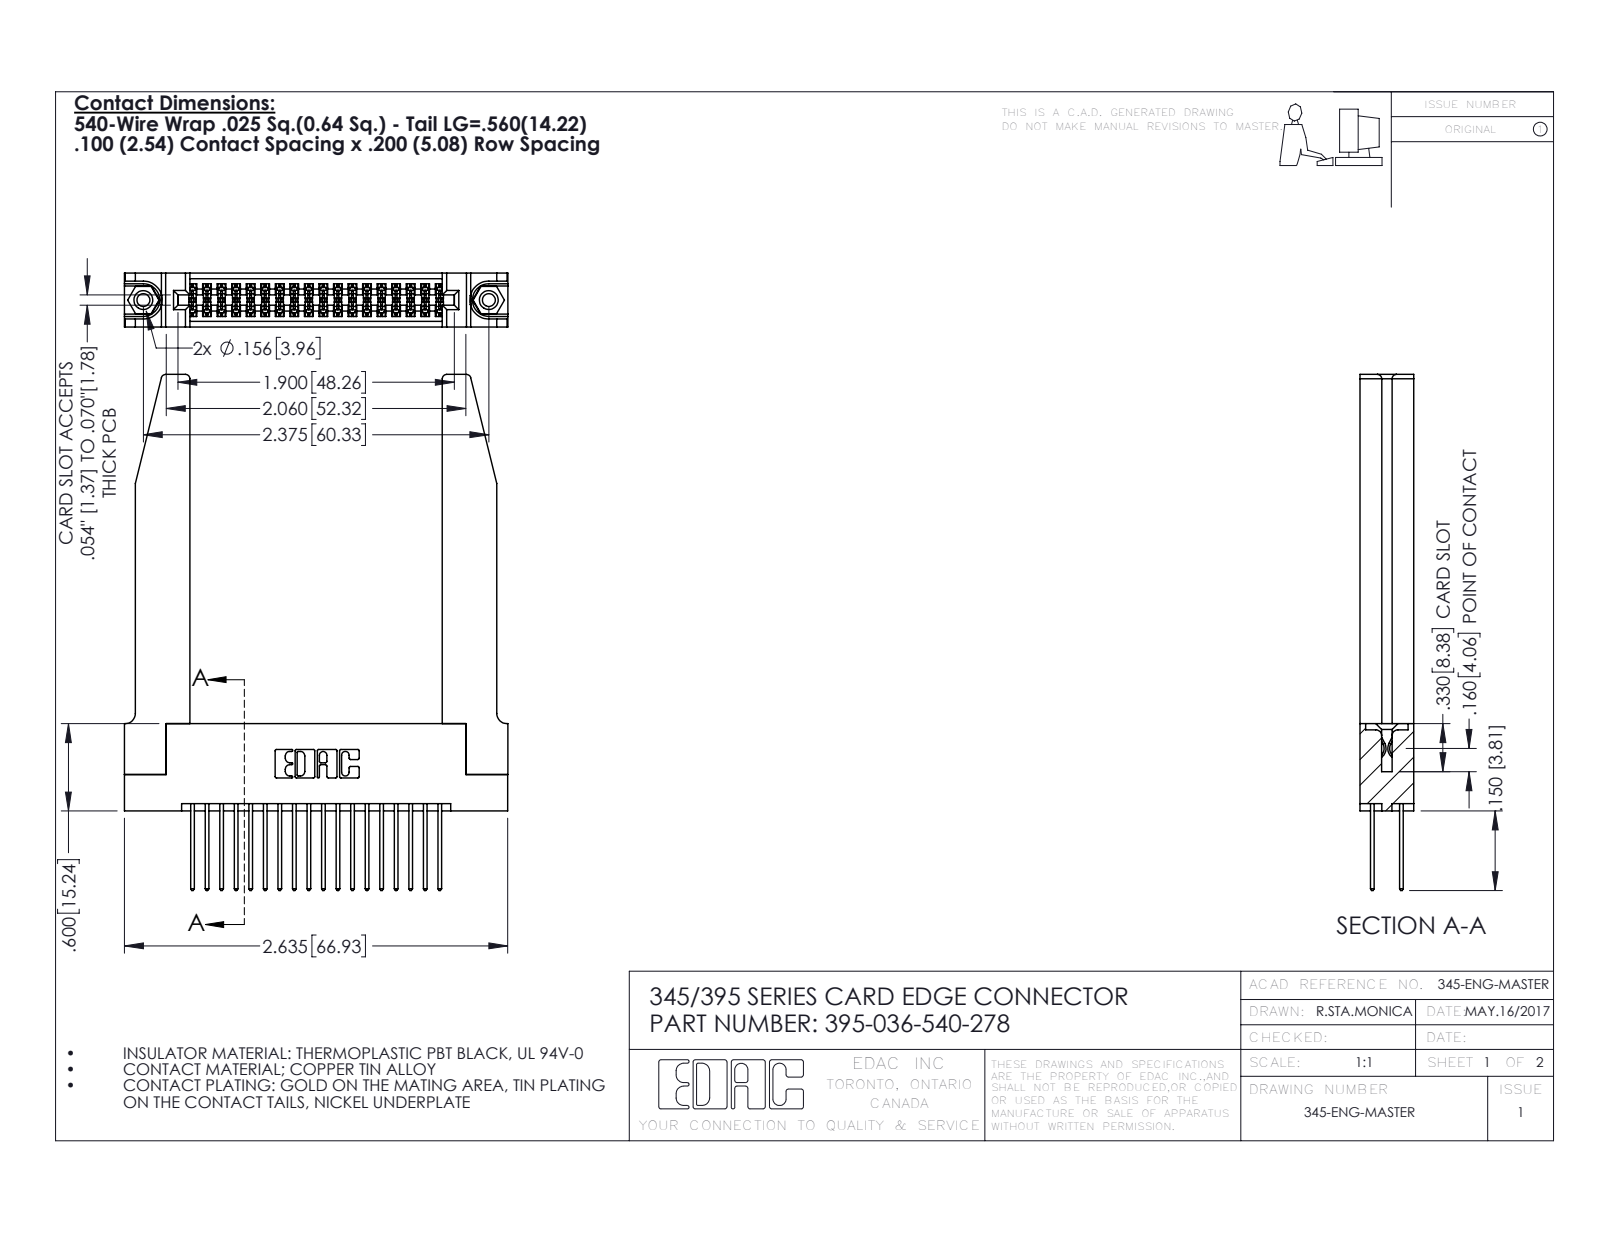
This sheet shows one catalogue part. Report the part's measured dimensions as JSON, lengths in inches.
{"part_name": "345-220-078_345-220-078; 395-036-540-278; 345-250-001_345-250-001-102; 345 Part_Flush Mounting Lugs - 0.156 Dia-TH (+1 more)", "step_written_by": "SolidWorks 2016 (CONFIG_CONTROL_DESIGN)", "units": "inches", "bodies": {"solids": 41, "faces": 2160, "planar": 1410, "cylindrical": 698, "other": 52}, "overall_size": [3.547, 2.636, 0.37], "volume_in3": 0.866, "surface_area_in2": 25.56, "round_holes": [[0.089, 2], [0.125, 2], [0.156, 2], [0.064, 1]], "round_bosses_or_shafts": [[0.155, 2]], "partial_cylinders_radius": [[0.006, 54], [0.01, 36], [0.01, 22], [0.03, 8], [0.007, 6], [0.031, 6], [0.026, 3], [0.014, 2]], "face_to_face_distances": [0.37, 0.072, 0.298, 0.2, 0.098, 0.272, 0.025, 0.225, 0.15, 0.148], "hole_center_spacings": [0.27, 2.141, 2.375]}
